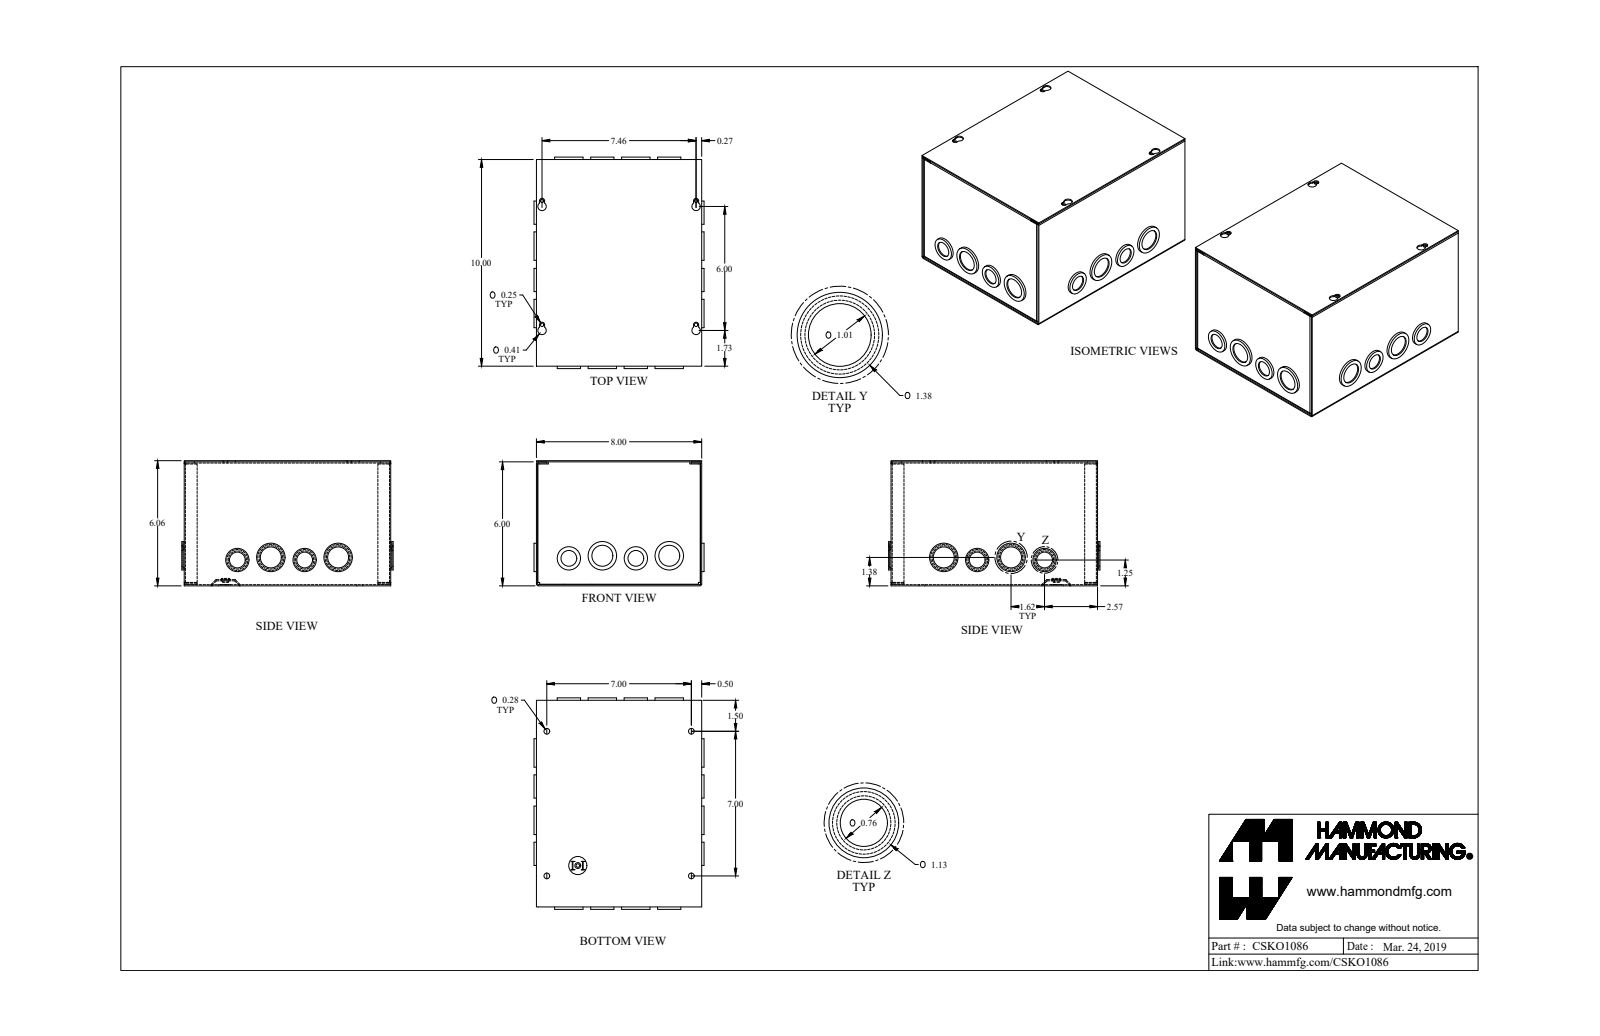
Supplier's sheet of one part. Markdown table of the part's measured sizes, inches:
| quantity | value |
| --- | --- |
| part name | CSKO1086_Default |
| STEP written by | SolidWorks 2019 (CONFIG_CONTROL_DESIGN) |
| units | inches |
| bodies | 4 solids, 397 faces (189 planar, 200 cylindrical, 8 other) |
| overall size | 10.234 × 8.234 × 6.057 |
| volume | 23.68 in³ |
| surface area | 840.7 in² |
| round holes (diameter × count) | 1.011 × 12, 0.761 × 6, 1.261 × 6, 0.17 × 5, 0.281 × 4, 0.5 × 1 |
| round bosses / shafts (diameter × count) | 1.375 × 6, 1.125 × 6, 1.125 × 6, 0.875 × 5, 0.875 × 3, 0.492 × 1, 0.284 × 1 |
| partial cylindrical surfaces (radius × count) | 0.029 × 12, 0.086 × 12, 0.057 × 8, 0.125 × 4, 0.203 × 4 |
| main face-to-face distances | 0.057, 6, 7.943, 5.943, 9.943, 6.057, 8, 7.886, 10, 9.886 |
| hole center spacings | 1.625, 0.125, 0.55, 1.62, 3.24, 3.242, 6.504, 7 |
